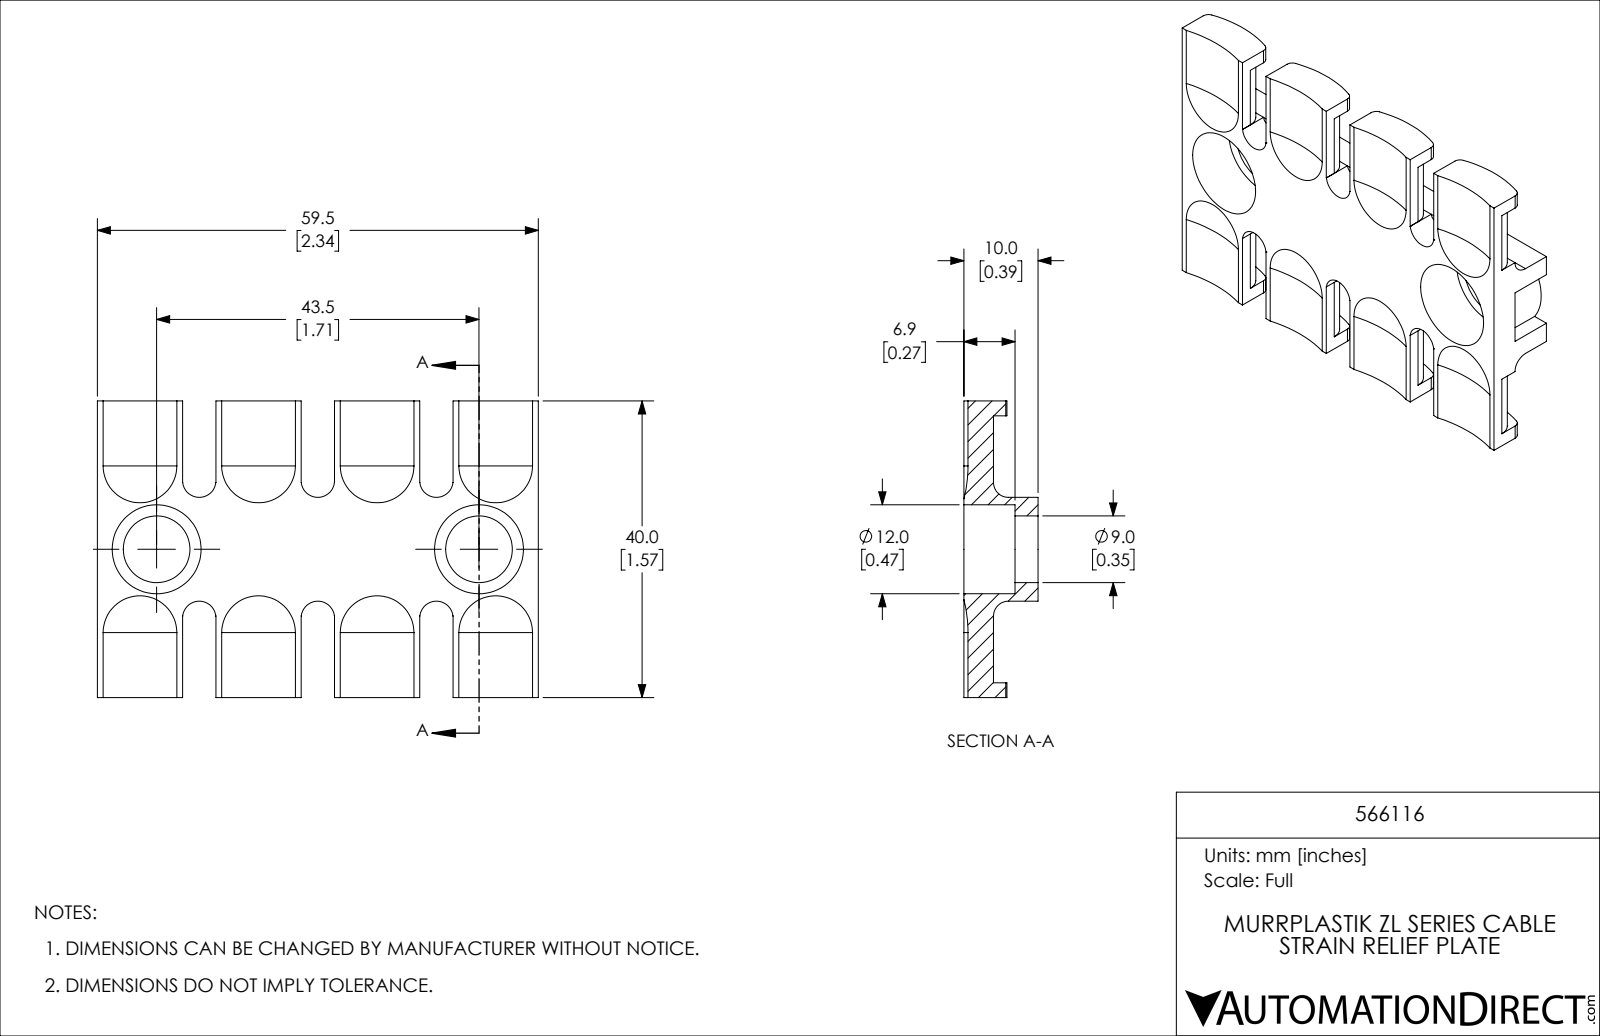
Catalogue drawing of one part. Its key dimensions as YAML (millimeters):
part_name: "566116"
step_written_by: "SolidWorks 2019 (CONFIG_CONTROL_DESIGN)"
units: millimeters
bodies: {solids: 1, faces: 161, planar: 66, cylindrical: 87, other: 8}
overall_size: [59.5, 40, 10]
volume: 9413
surface_area: 7369
round_holes:
  - {diameter: 9, count: 2}
  - {diameter: 12, count: 2}
partial_cylinders:
  - {radius: 1, count: 8}
  - {radius: 2.5, count: 8}
  - {radius: 2.25, count: 6}
  - {radius: 16, count: 4}
  - {radius: 18, count: 4}
  - {radius: 2, count: 2}
  - {radius: 7, count: 2}
face_to_face_distances: [4, 16, 11, 13, 27, 6, 10, 24, 3, 14]
hole_center_spacings: [43.5]
